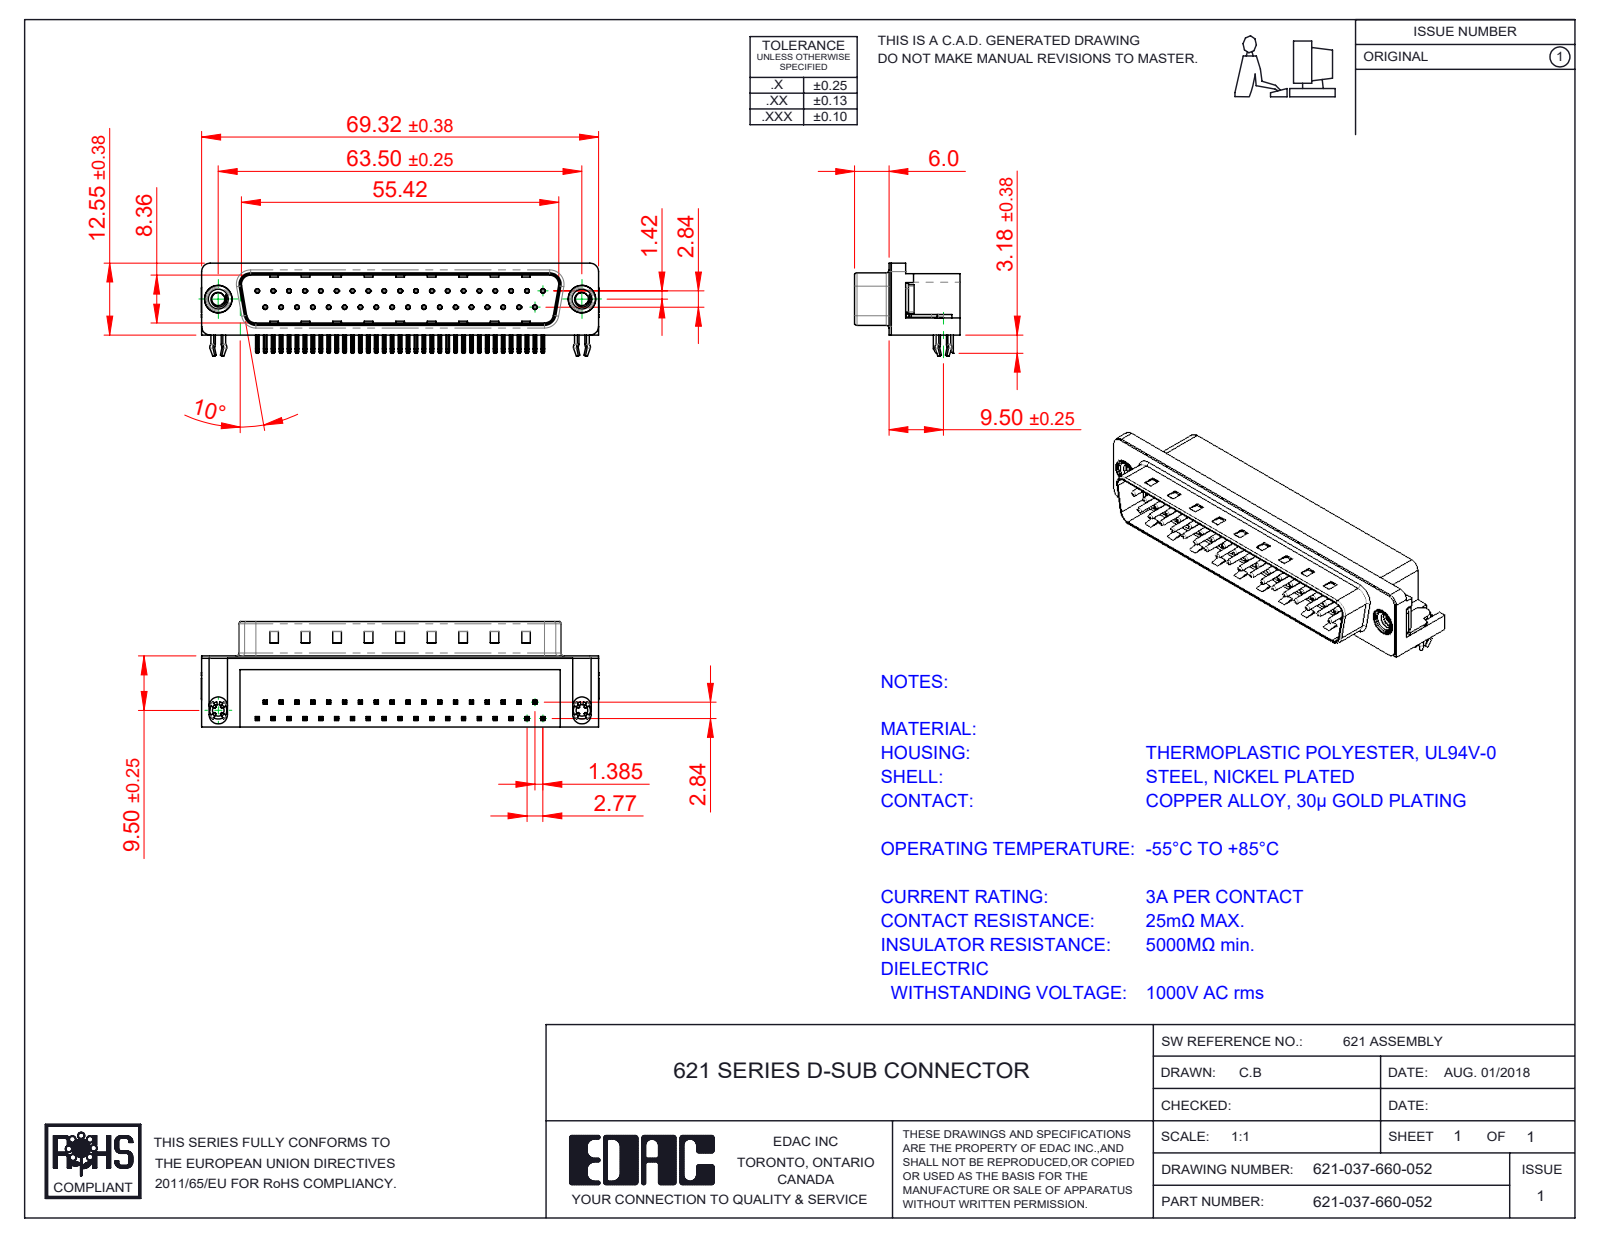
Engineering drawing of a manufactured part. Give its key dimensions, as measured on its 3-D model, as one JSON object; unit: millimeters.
{"part_name": "621-037-660-052; 621 Contact Bottom; 621 4-40 Threaded Board Mount; 621 Housing_37 Socket (+3 more)", "step_written_by": "SolidWorks 2016 (CONFIG_CONTROL_DESIGN)", "units": "millimeters", "bodies": {"solids": 43, "faces": 3229, "planar": 2013, "cylindrical": 927, "other": 289}, "overall_size": [69.4, 18.4, 15.73], "volume_mm3": 8634, "surface_area_mm2": 10174, "round_holes": [[0.35, 37], [0.8, 37], [2.26, 4], [4, 2], [4.8, 2], [5, 2]], "round_bosses_or_shafts": [[0.75, 37], [4.9, 2], [4.75, 2], [3.9, 2], [3.26, 2]], "partial_cylinders_radius": [[0.25, 156], [0.12, 74], [1, 16], [0.5, 9], [1.6, 8], [1.5, 7], [0.9, 4], [2, 4]], "face_to_face_distances": [0.4, 12, 10.35, 8.76, 2.1, 1.7, 10.46, 10.86, 9, 12.4], "hole_center_spacings": [3.16, 2.77, 5.54, 8.31, 11.08, 13.85, 19.39, 22.16]}
